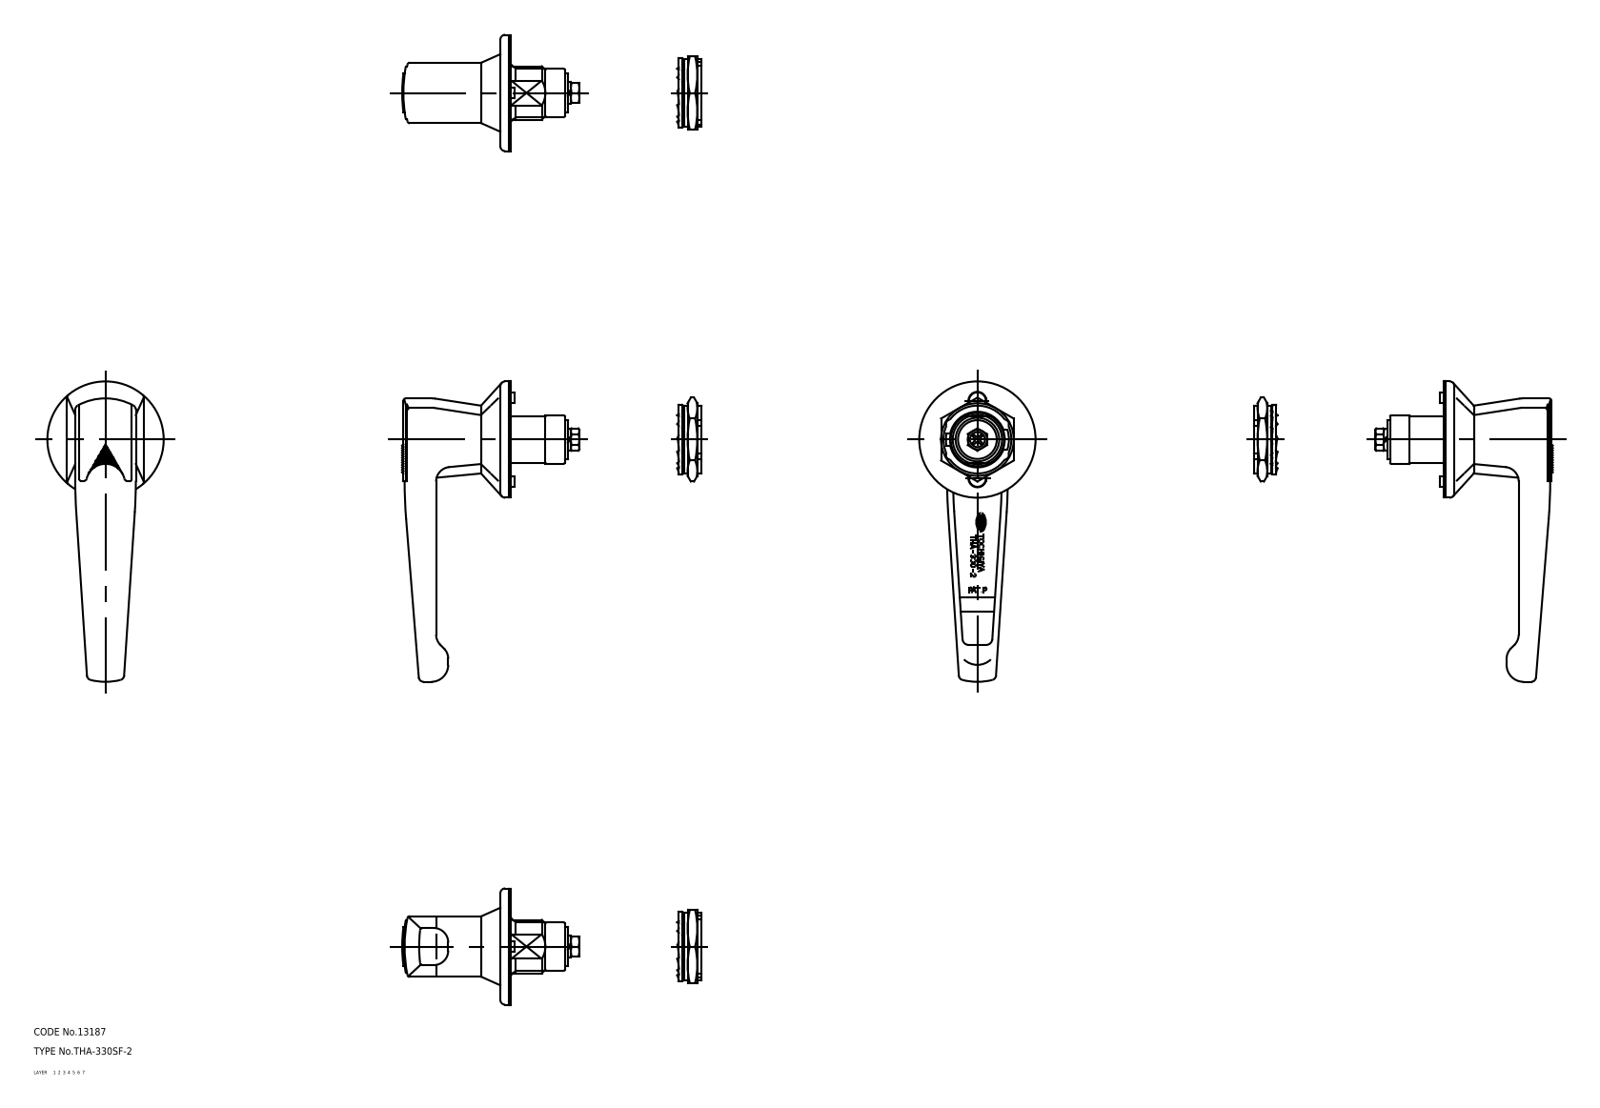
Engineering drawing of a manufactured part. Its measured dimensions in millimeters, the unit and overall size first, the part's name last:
Units: millimetres
Overall size (bounding box): 124 × 73.1 × 48
Volume: 56 923 mm³ · Surface area: 26 503 mm²
Bodies: 8 solids, 319 faces (0 planar, 0 cylindrical, 319 other)
Part name (STEP PRODUCT): washer_B; washer_A; spacer; packing (+5 more)
STEP written by: CADfix (AUTOMOTIVE_DESIGN)
